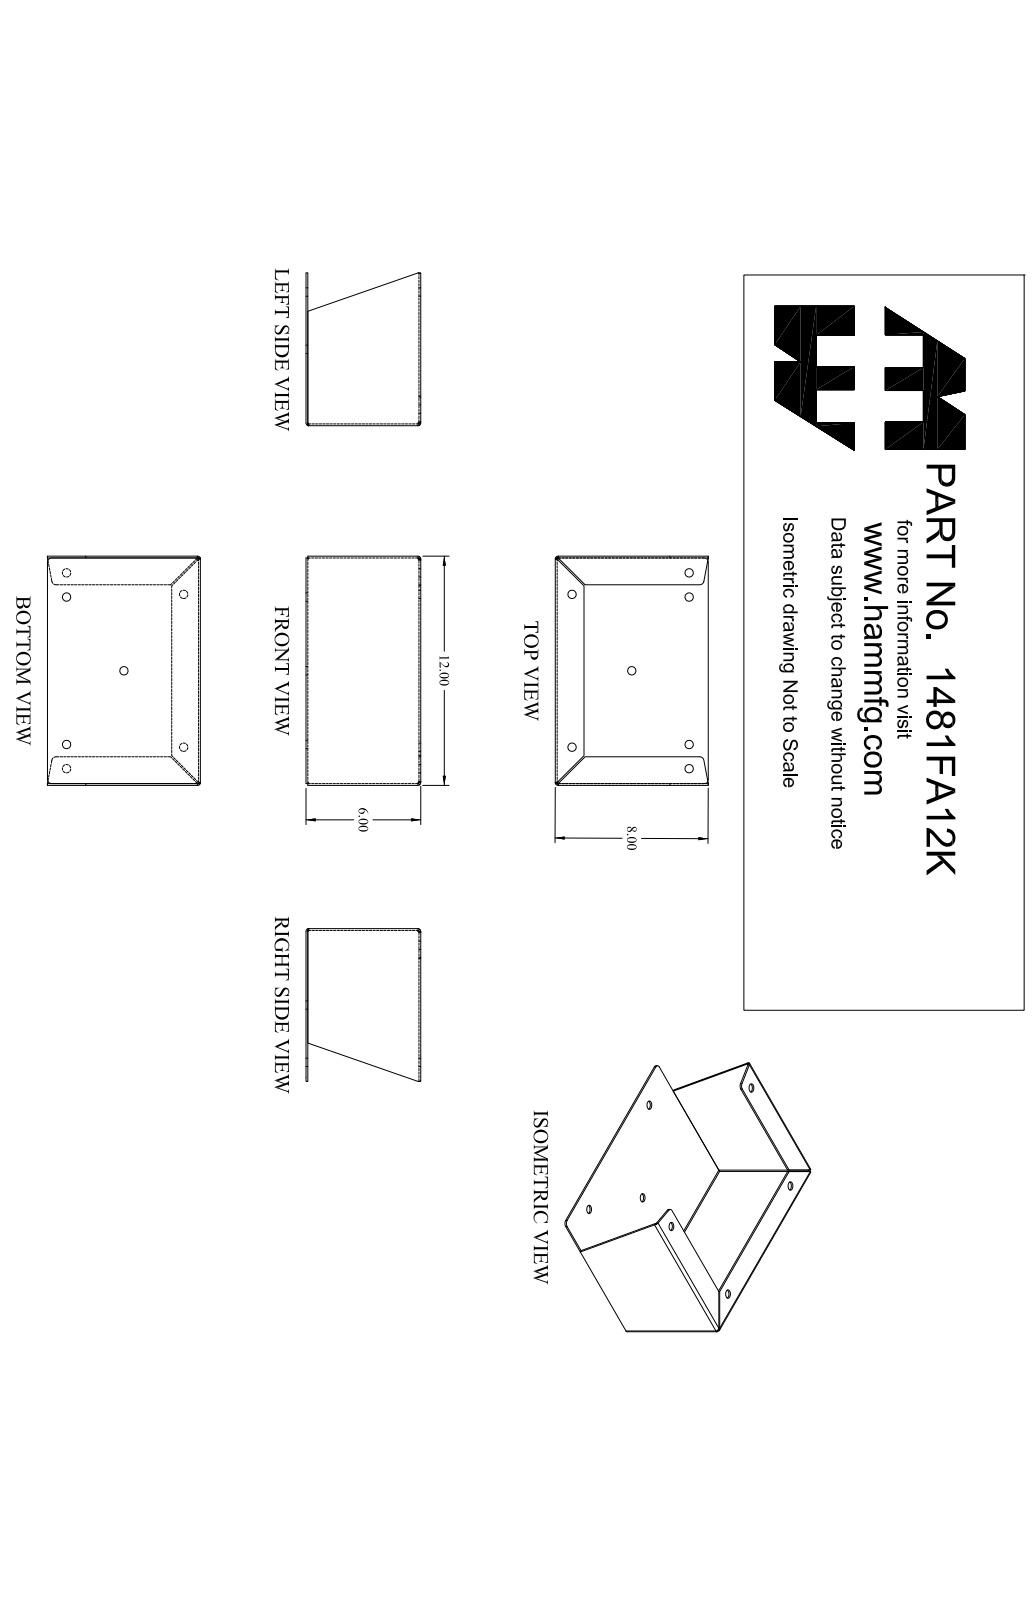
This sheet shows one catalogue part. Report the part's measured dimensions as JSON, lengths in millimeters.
{"part_name": "1481FA12K_Default", "step_written_by": "SolidWorks 2019 (CONFIG_CONTROL_DESIGN)", "units": "millimeters", "bodies": {"solids": 1, "faces": 78, "planar": 42, "cylindrical": 30, "other": 6}, "overall_size": [304.8, 203.2, 152.4], "volume_mm3": 432800, "surface_area_mm2": 364600, "round_holes": [[11.1, 7]], "partial_cylinders_radius": [[1.2, 6], [3.6, 6], [5.6, 4]], "face_to_face_distances": [2.4, 2.4, 302.4, 304.8, 300, 147.6, 150, 150, 152.4, 38.1], "hole_center_spacings": [124.2, 128.9, 155.6, 158.2, 253.1, 32.2, 32.2, 150.9]}
